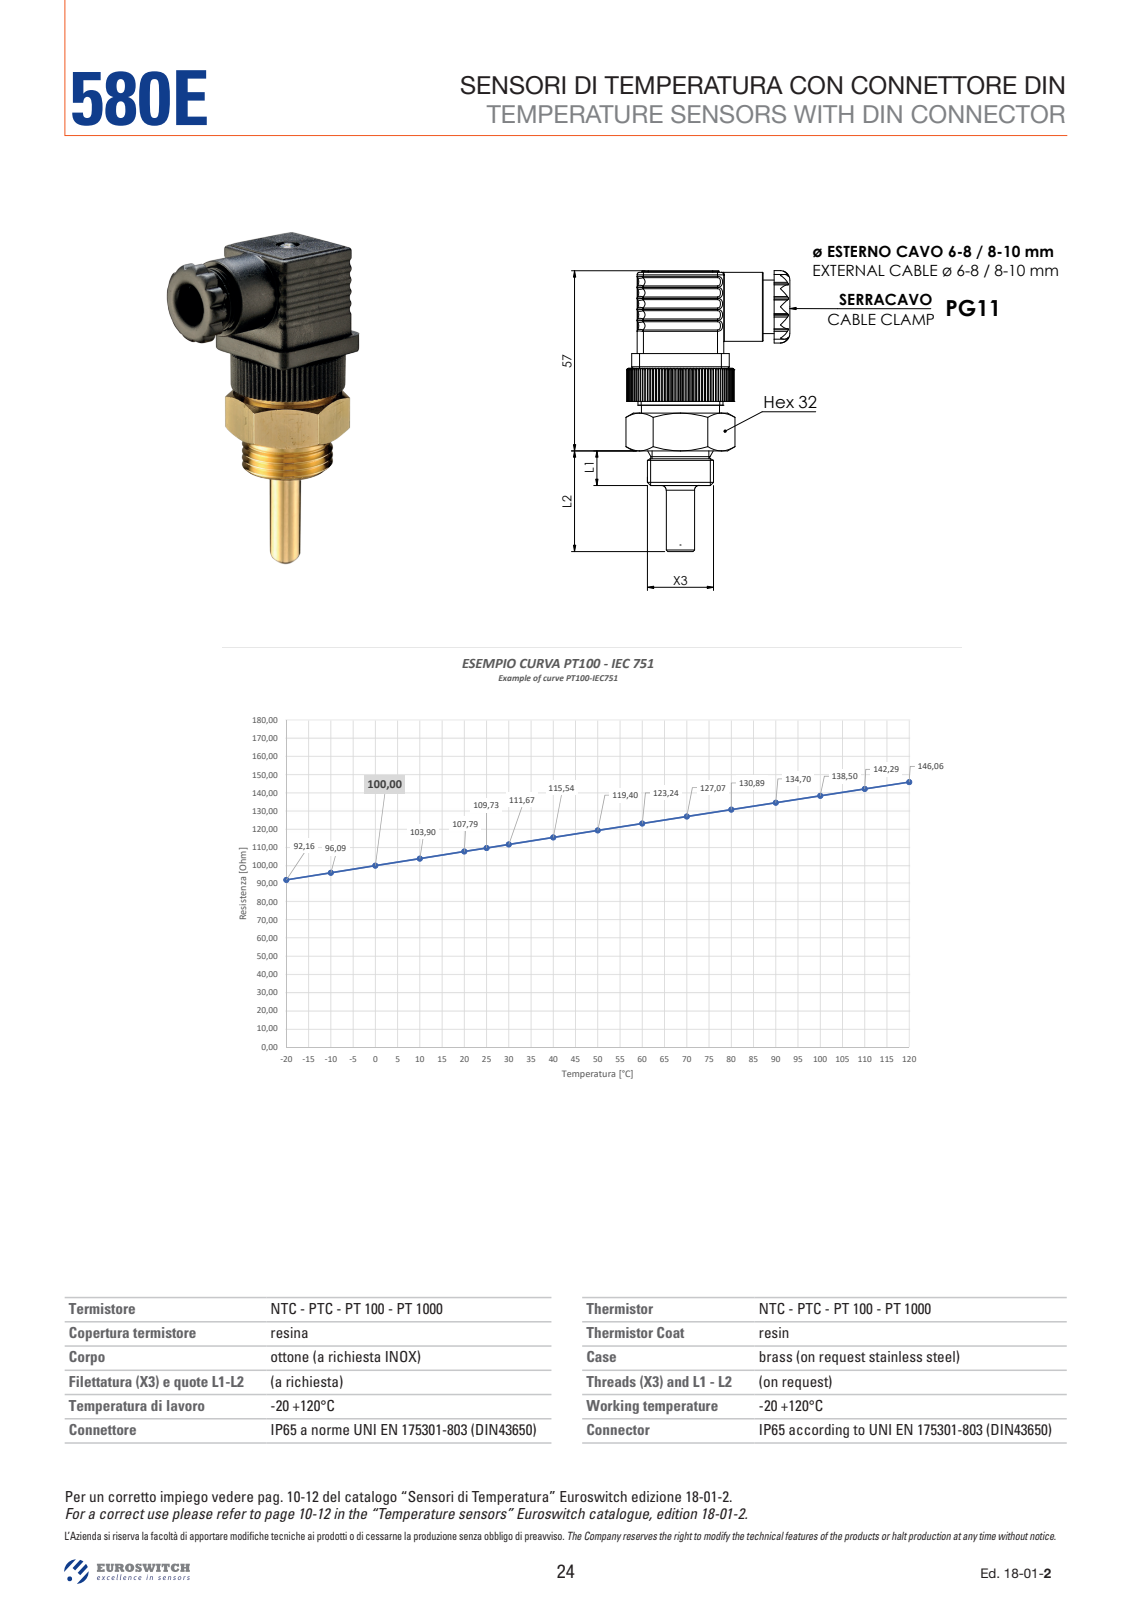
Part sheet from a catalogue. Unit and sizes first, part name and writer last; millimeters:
Units: millimetres
Overall size (bounding box): 70.25 × 34.64 × 33.99
Round holes (diameter × count): ⌀1.3 ×2, ⌀2.6 ×1, ⌀3.5 ×1, ⌀22.14 ×1
Round bosses / shafts (diameter × count): ⌀27 ×1, ⌀24.8 ×1, ⌀21.6 ×1, ⌀21 ×1, ⌀9 ×1, ⌀7.9 ×1, ⌀4 ×1, ⌀3.5 ×1
Partial cylindrical surfaces — rounded edges, fillets, slot ends (radius × count): R0.2 ×6, R1 ×6, R17 ×1
Main face-to-face distances: 30, 21.22, 26.25, 15.75, 10.5, 12, 21.2, 14.25, 3.75, 37.25
Bodies: 0 solids, 647 faces (366 planar, 142 cylindrical, 139 other)
Part name (STEP PRODUCT): 580E
STEP written by: SolidWorks 2019 (AUTOMOTIVE_DESIGN)
